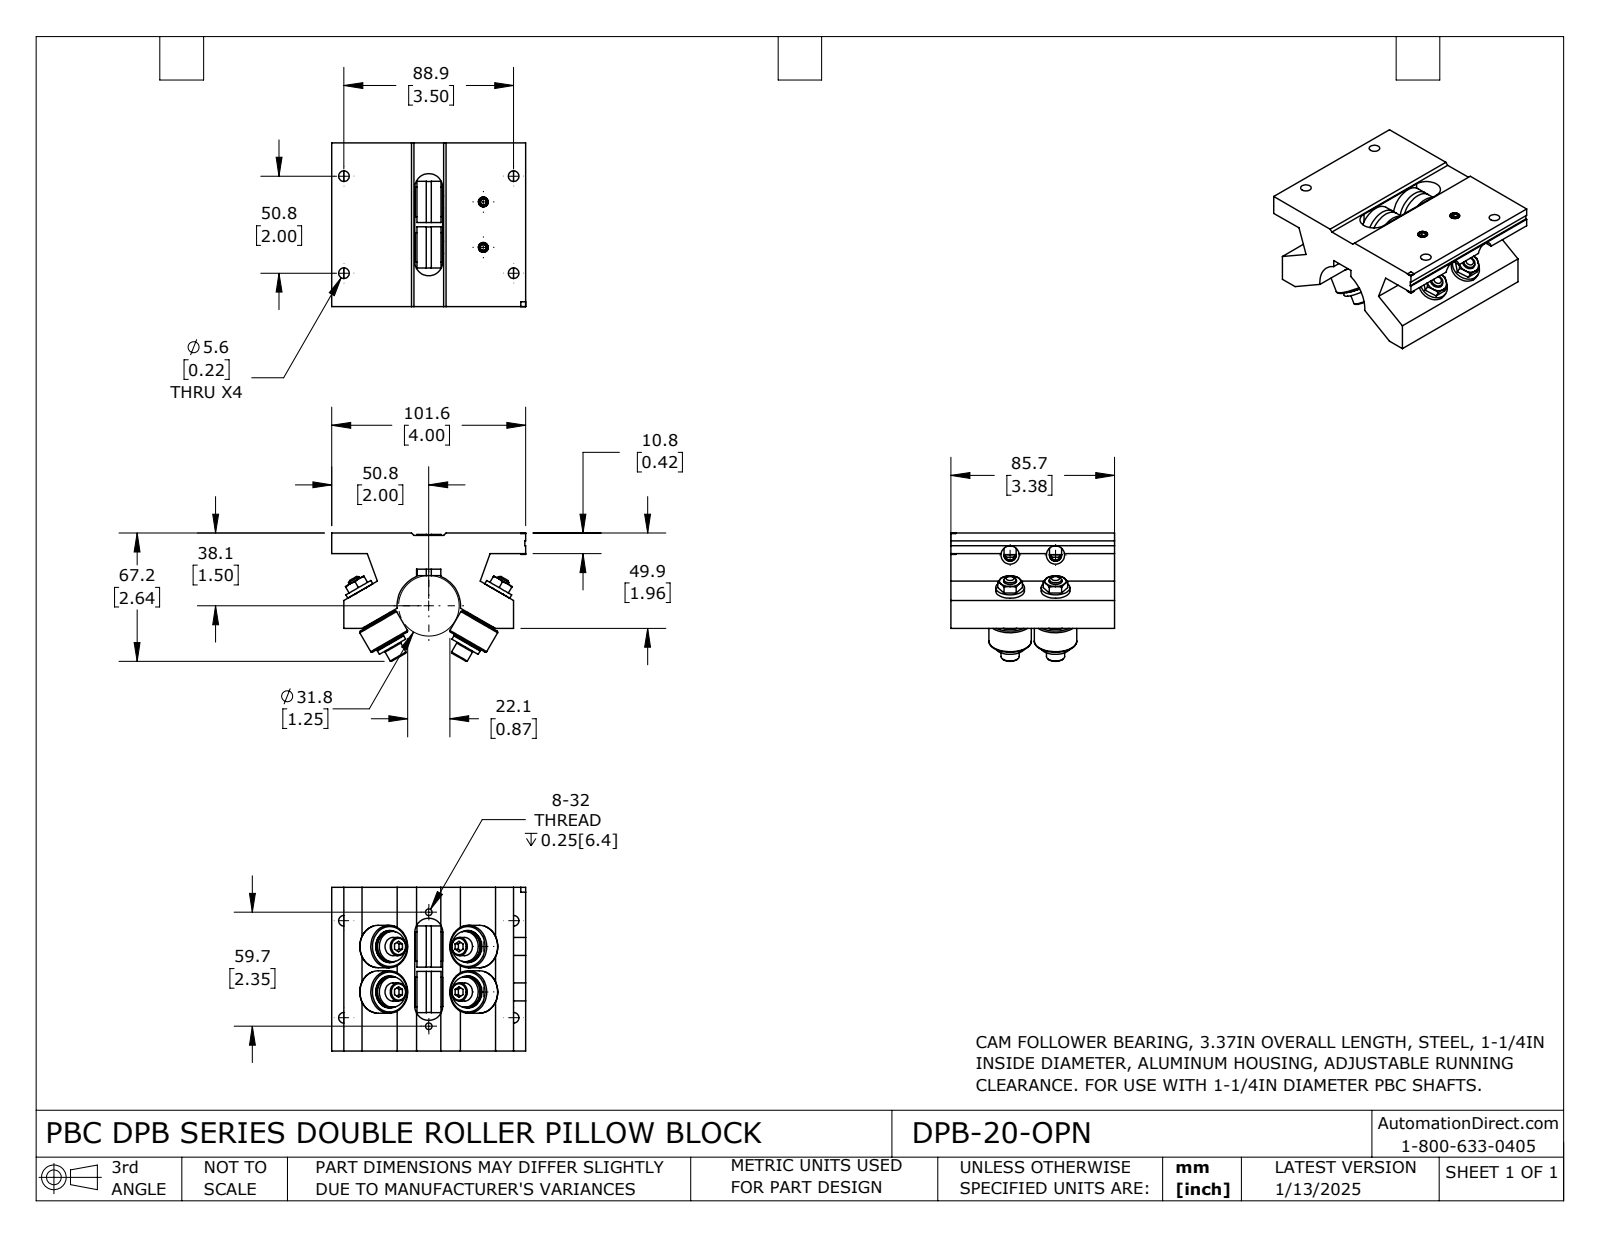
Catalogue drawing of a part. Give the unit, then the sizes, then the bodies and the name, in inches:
Units: inches
Overall size (bounding box): 4 × 3.375 × 2.644
Round holes (diameter × count): ⌀0.185 ×4, ⌀0.219 ×4, ⌀0.25 ×4, ⌀0.25 ×4, ⌀0.281 ×4, ⌀0.287 ×4, ⌀0.382 ×4, ⌀0.645 ×4, ⌀0.136 ×2, ⌀0.201 ×2, ⌀0.219 ×2, ⌀0.249 ×2
Round bosses / shafts (diameter × count): ⌀0.875 ×4, ⌀0.594 ×4, ⌀0.378 ×4, ⌀0.375 ×4, ⌀0.25 ×4, ⌀0.85 ×2, ⌀0.625 ×2, ⌀0.625 ×2
Partial cylindrical surfaces — rounded edges, fillets, slot ends (radius × count): R0.288 ×2, R0.655 ×1
Main face-to-face distances: 0.685, 3.375, 0.424, 0.25, 1.54, 1.964, 1.463, 2.037, 3.75, 2.287
Hole centre spacings: 0.937, 1.759, 2.791, 0.02, 0.82, 0.937, 1.328, 1.596
Volume: 16.29 in³ · Surface area: 111.9 in²
Bodies: 27 solids, 677 faces (225 planar, 226 cylindrical, 226 other)
Part name (STEP PRODUCT): DPB-20-OPN
STEP written by: SolidWorks 2023 (CONFIG_CONTROL_DESIGN)
